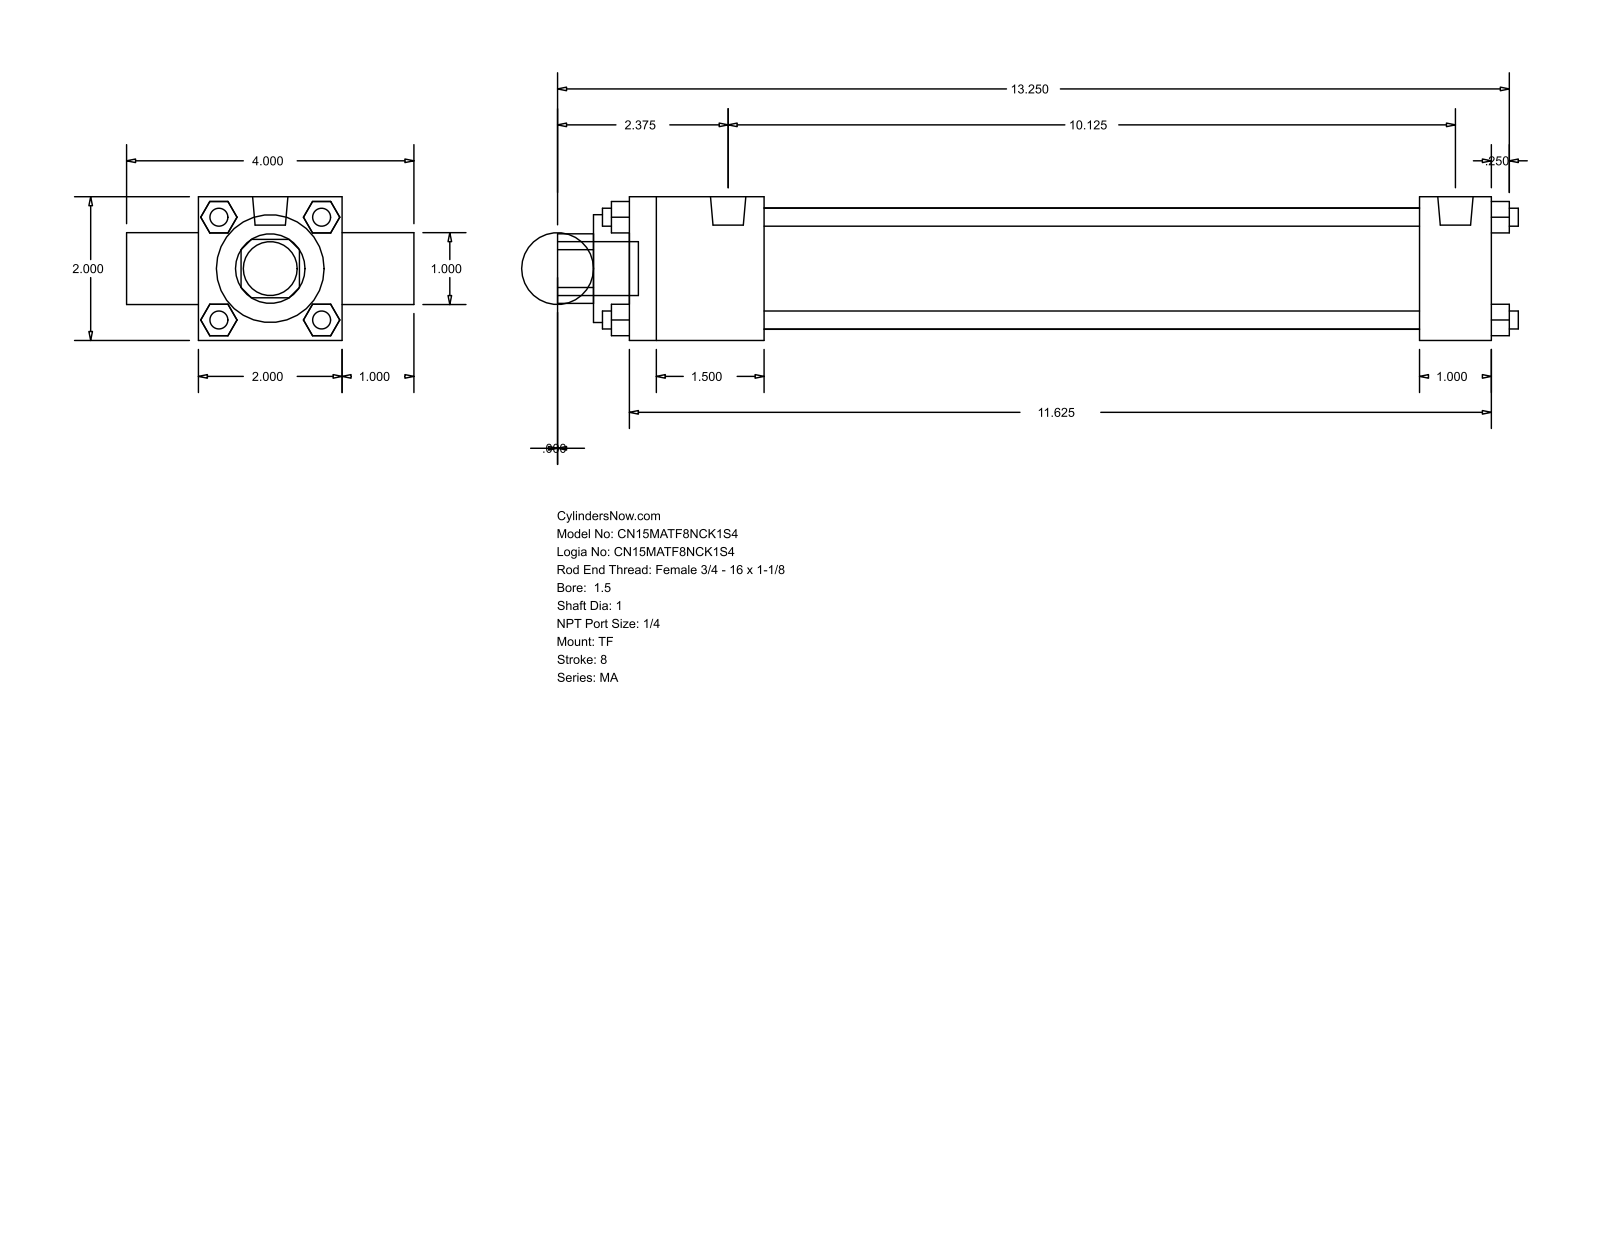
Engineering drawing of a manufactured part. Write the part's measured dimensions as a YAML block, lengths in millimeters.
part_name: "MA_TF__0150_1"
step_written_by: "GSSL Pune (CONFIG_CONTROL_DESIGN)"
units: millimeters
bodies: {solids: 0, faces: 120, planar: 92, cylindrical: 28, other: 0}
overall_size: [339.73, 101.6, 50.8]
round_holes:
  - {diameter: 25.4, count: 2}
  - {diameter: 38.1, count: 1}
  - {diameter: 42.93, count: 1}
round_bosses_or_shafts:
  - {diameter: 6.35, count: 4}
  - {diameter: 7.94, count: 3}
  - {diameter: 12.49, count: 2}
  - {diameter: 19.05, count: 1}
partial_cylinders:
  - {radius: 12.29, count: 1}
face_to_face_distances: [50.8, 25.4, 304.8, 76.2, 6.35, 47.63, 279.4, 231.77, 257.17, 317.5]
